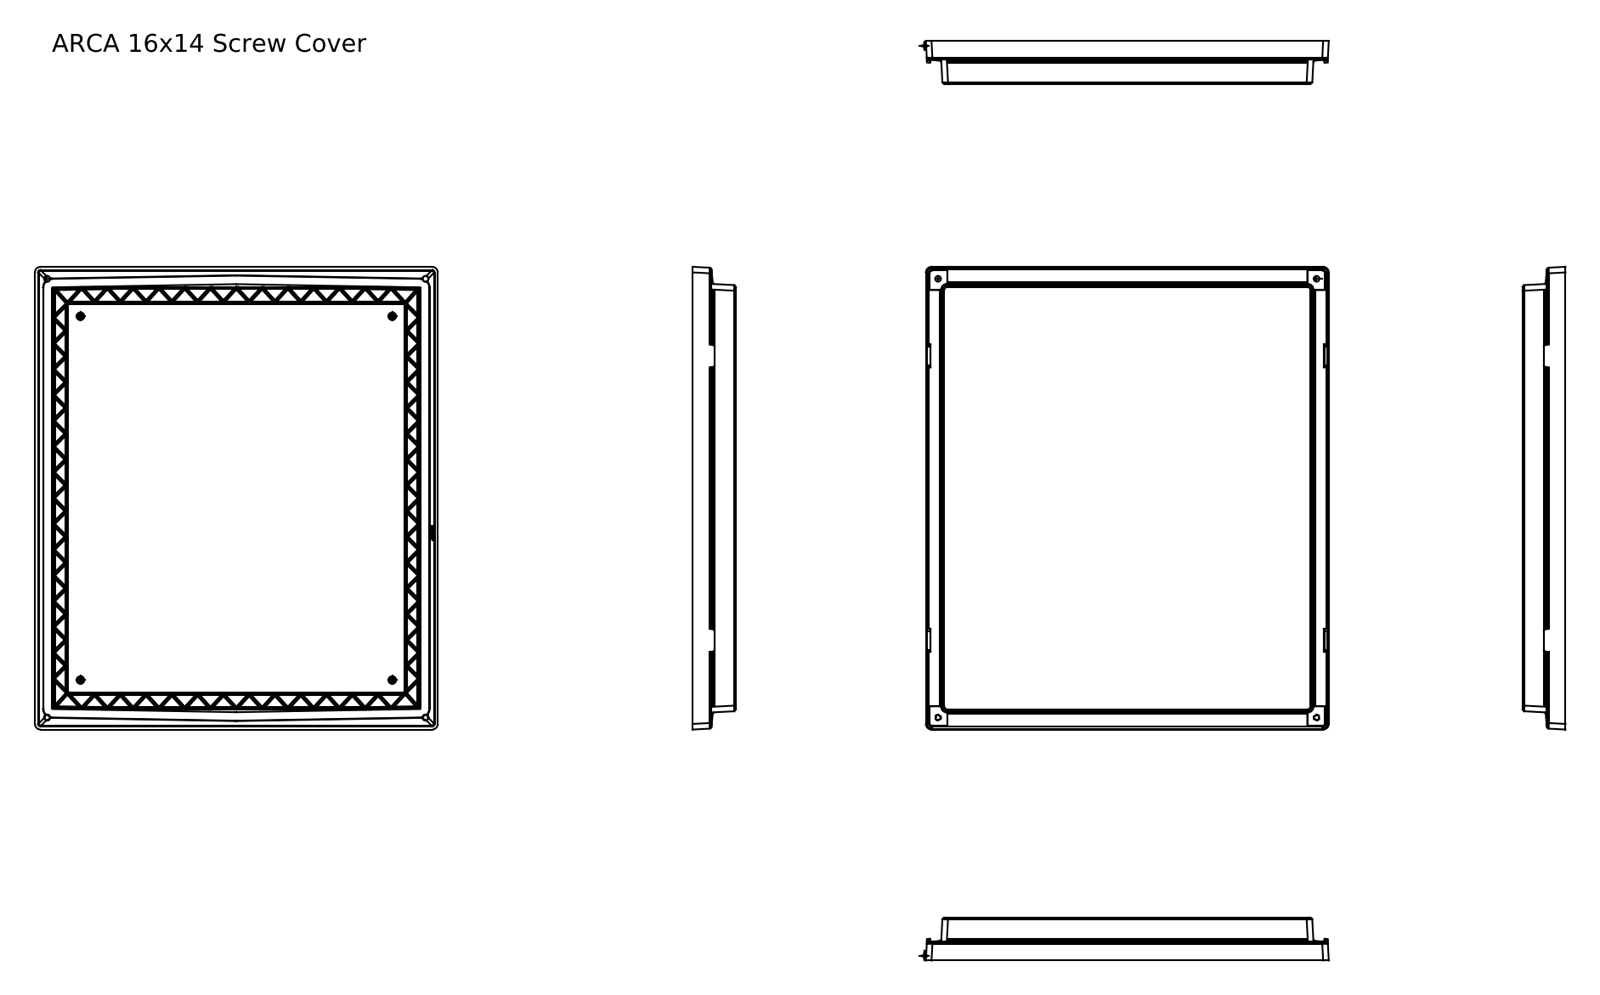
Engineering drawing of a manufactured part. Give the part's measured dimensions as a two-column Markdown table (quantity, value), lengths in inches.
| quantity | value |
| --- | --- |
| part name | 16x14_screw_cover |
| STEP written by | SolidWorks 2015 (AUTOMOTIVE_DESIGN) |
| units | inches |
| bodies | 1 solid, 909 faces (641 planar, 152 cylindrical, 116 other) |
| overall size | 17.809 × 15.506 × 1.654 |
| volume | 67.8 in³ |
| surface area | 1 023 in² |
| partial cylindrical surfaces (radius × count) | 0.079 × 16, 0.039 × 12, 0.059 × 4, 0.098 × 4, 0.217 × 4, 0.346 × 4, 0.906 × 4, 1.043 × 4 |
| main face-to-face distances | 0.142, 0.118, 0.731, 2.104, 2.925, 13.052, 2.194, 1.403, 0.702, 0.131 |
